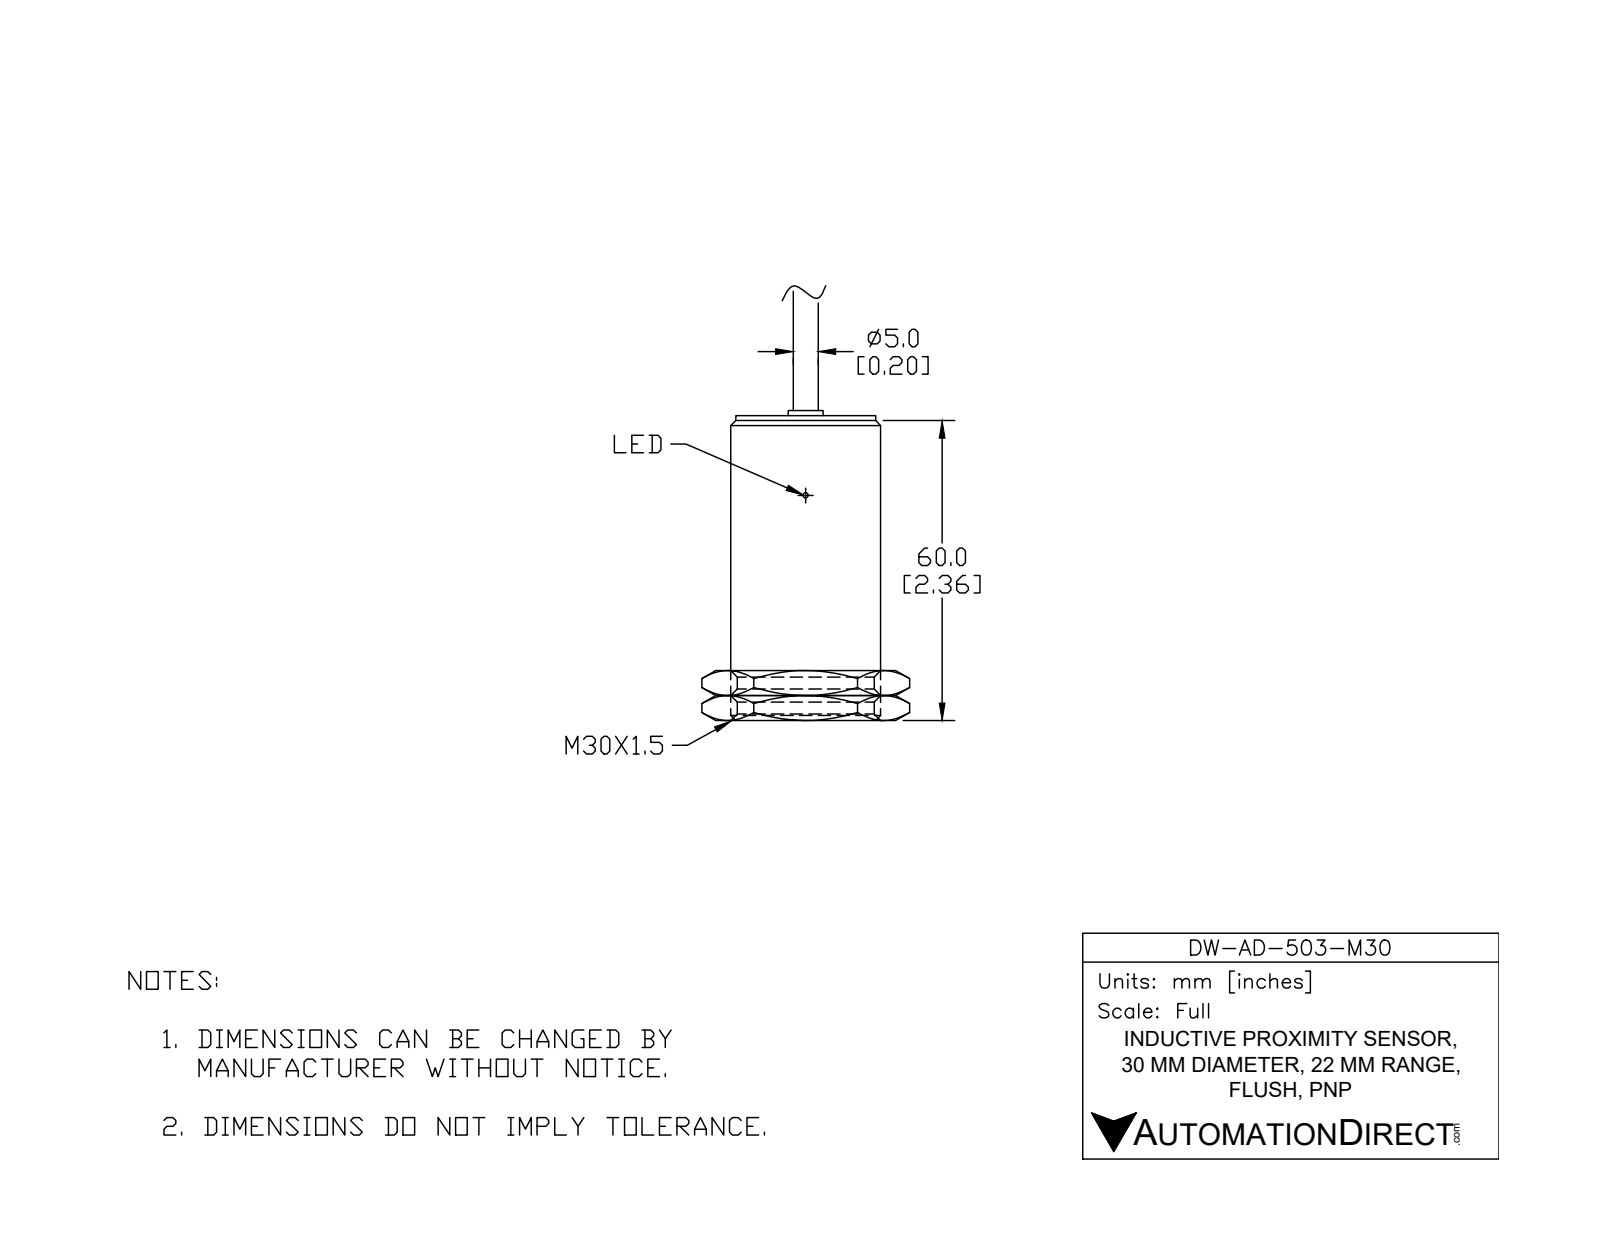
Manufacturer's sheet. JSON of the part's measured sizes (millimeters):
{"part_name": "DW-AD-503-M30", "step_written_by": "SolidWorks 2017 (AUTOMOTIVE_DESIGN)", "units": "millimeters", "bodies": {"solids": 2, "faces": 31, "planar": 17, "cylindrical": 5, "other": 9}, "overall_size": [86.6, 30, 30], "volume_mm3": 43560, "surface_area_mm2": 7535, "round_bosses_or_shafts": [[30, 1], [27.5, 1], [10.5, 1], [6.8, 1], [5, 1]], "face_to_face_distances": [61, 63, 2, 0.8, 61.8, 1.2, 58, 3, 3.8, 5]}
